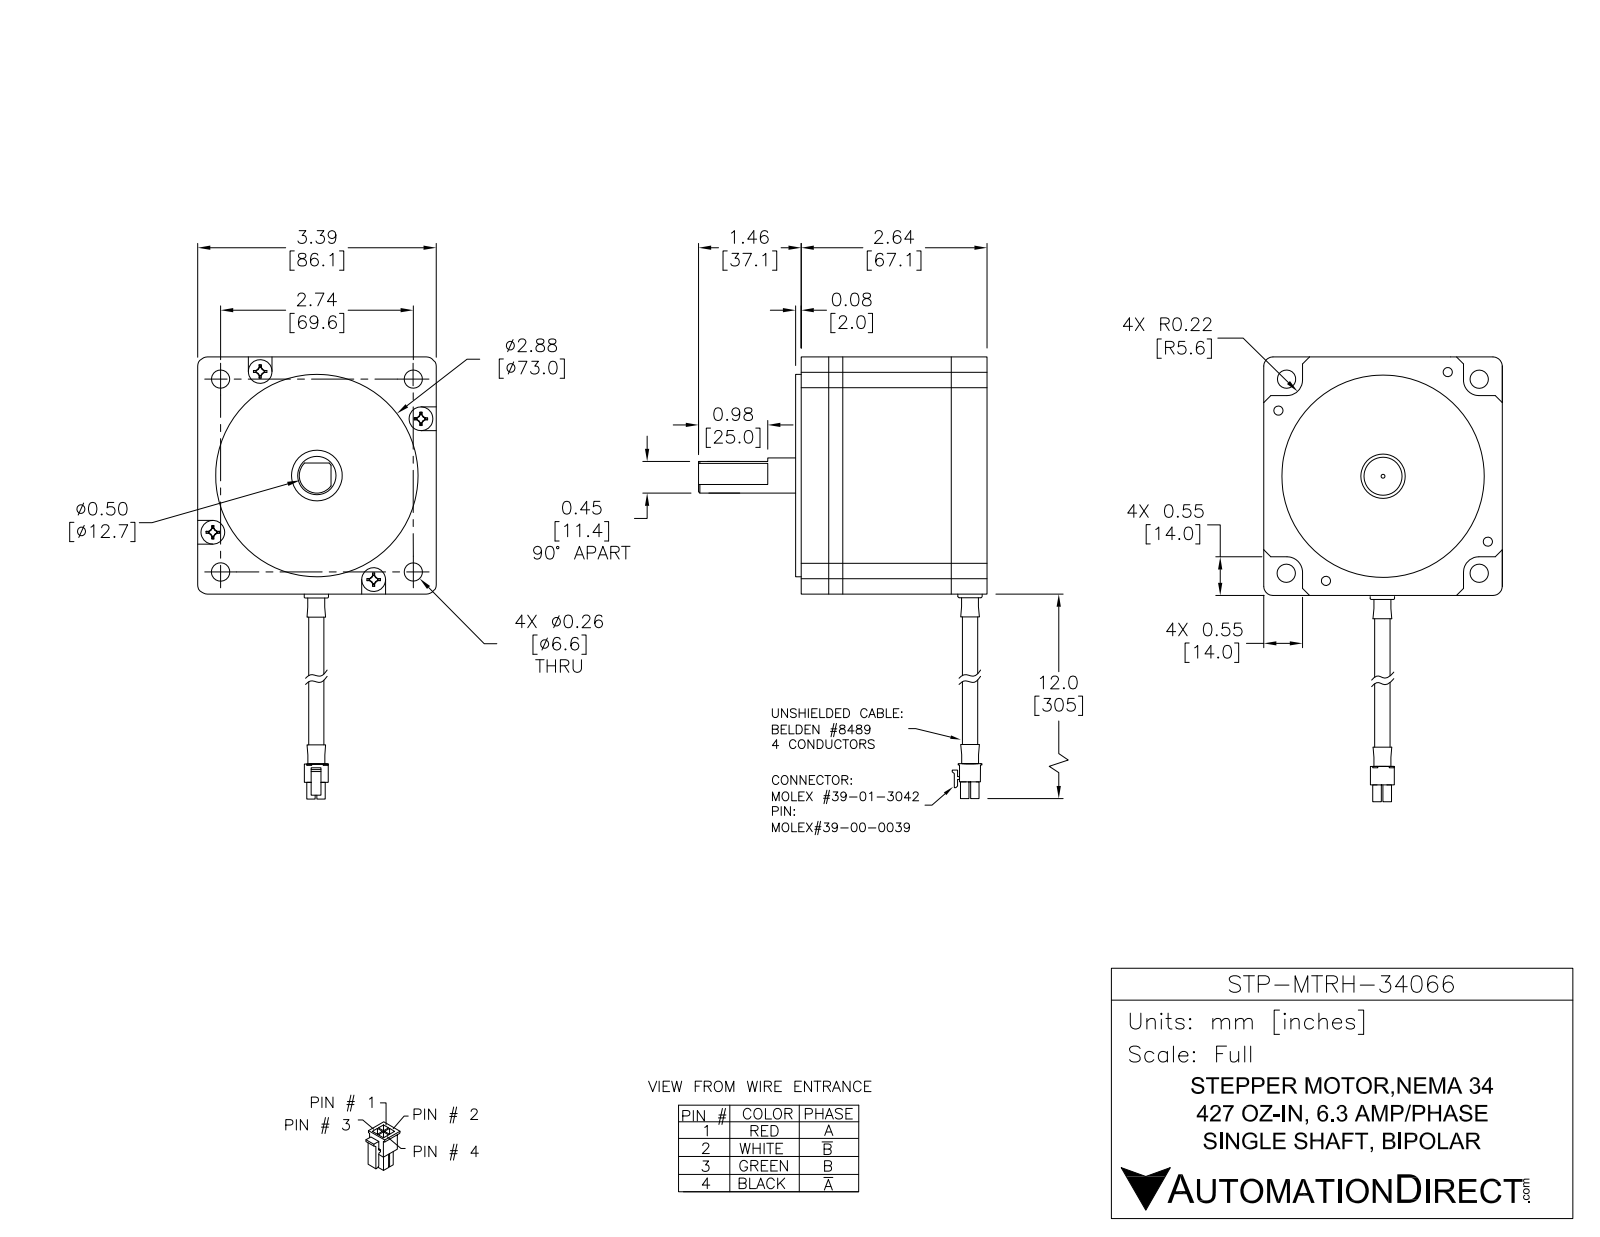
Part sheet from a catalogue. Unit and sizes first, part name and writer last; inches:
Units: inches
Overall size (bounding box): 6.185 × 4.06 × 3.37
Round holes (diameter × count): ⌀0.26 ×4
Round bosses / shafts (diameter × count): ⌀0.05 ×4, ⌀2.875 ×1, ⌀0.5 ×1
Partial cylindrical surfaces — rounded edges, fillets, slot ends (radius × count): R0.1 ×8, R1.94 ×1
Main face-to-face distances: 3.37, 0.574, 2.796, 2.66, 2.6, 0.06, 2.222, 0.4, 0.46, 2.2
Hole centre spacings: 2.74, 3.875
Volume: 27.1 in³ · Surface area: 61.46 in²
Bodies: 1 solid, 67 faces (28 planar, 36 cylindrical, 3 other)
Part name (STEP PRODUCT): STP-MTRH-34066
STEP written by: SolidWorks 2014 (AUTOMOTIVE_DESIGN)
